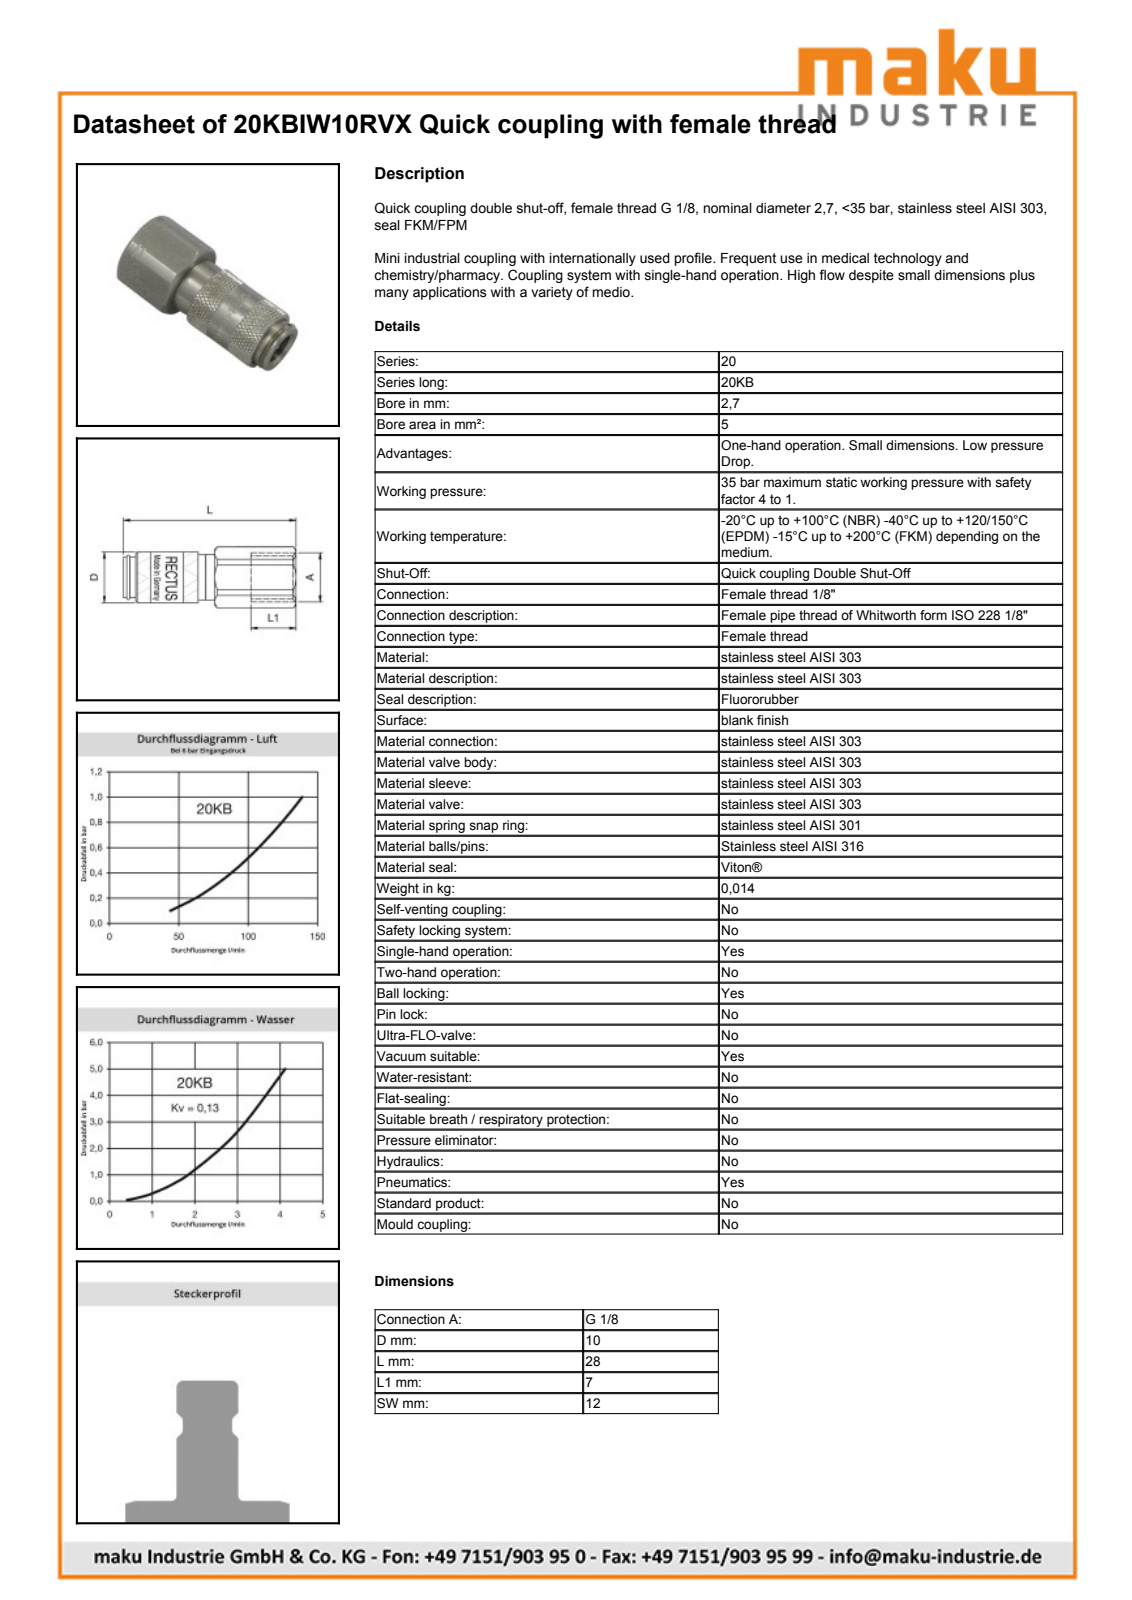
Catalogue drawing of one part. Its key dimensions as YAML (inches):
part_name: "D110182"
step_written_by: "Autodesk Inventor 2013 (AUTOMOTIVE_DESIGN)"
units: inches
bodies: {solids: 2, faces: 406, planar: 147, cylindrical: 59, other: 200}
overall_size: [1.104, 0.512, 0.486]
volume: 0.124
surface_area: 3.598
round_holes:
  - {diameter: 0.157, count: 1}
  - {diameter: 0.294, count: 1}
  - {diameter: 0.319, count: 1}
  - {diameter: 0.321, count: 1}
  - {diameter: 0.337, count: 1}
  - {diameter: 0.36, count: 1}
  - {diameter: 0.362, count: 1}
round_bosses_or_shafts:
  - {diameter: 0.407, count: 1}
  - {diameter: 0.394, count: 1}
  - {diameter: 0.354, count: 1}
  - {diameter: 0.315, count: 1}
  - {diameter: 0.307, count: 1}
  - {diameter: 0.291, count: 1}
  - {diameter: 0.287, count: 1}
  - {diameter: 0.279, count: 1}
partial_cylinders:
  - {radius: 0.193, count: 1}
  - {radius: 0.256, count: 1}
face_to_face_distances: [0.472, 0.12, 0.709, 0.829, 0.276, 1.104, 0.396, 0.13, 0.526, 0.197]
